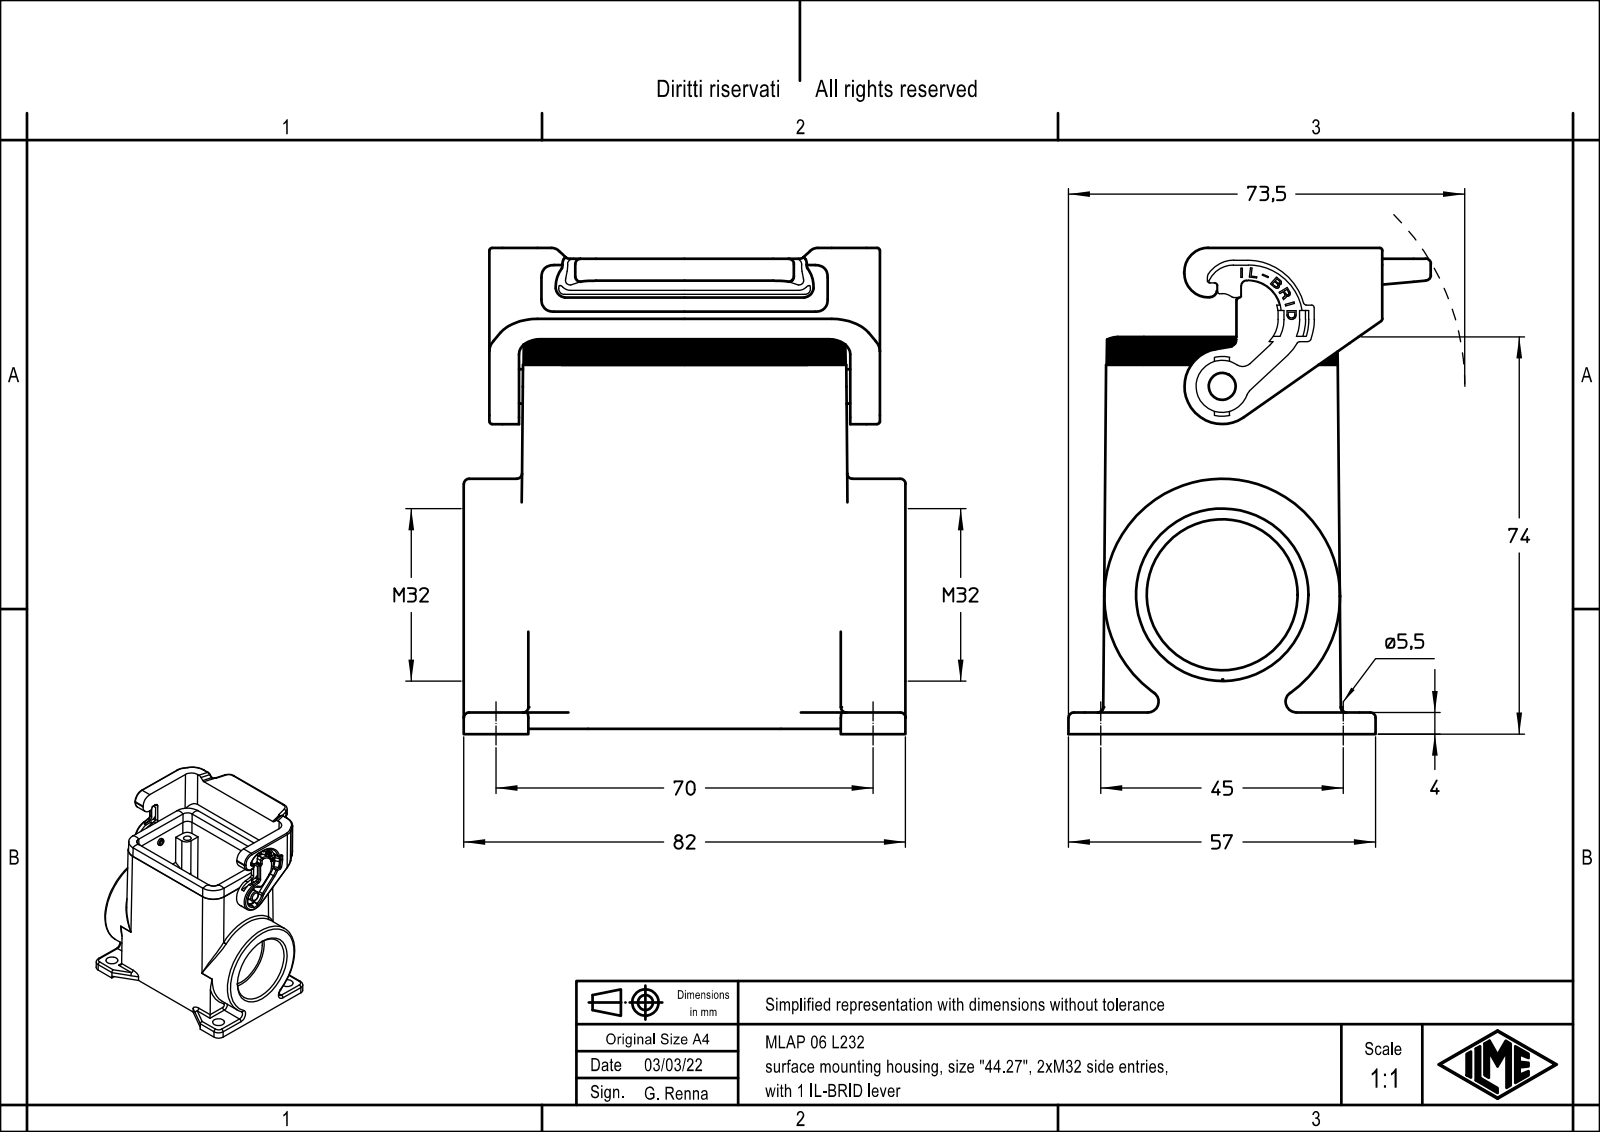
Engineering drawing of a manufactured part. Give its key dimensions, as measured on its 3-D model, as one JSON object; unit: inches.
{"part_name": "MLAP_06_L232", "step_written_by": "Creo Elements/Direct Modeling 20.1B 02-Apr-2019 (C) Parametric Technology GmbH (AUTOMOTIVE_DESIGN)", "units": "inches", "bodies": {"solids": 1, "faces": 708, "planar": 449, "cylindrical": 191, "other": 68}, "overall_size": [3.551, 3.228, 2.648], "volume_in3": 6.236, "surface_area_in2": 70.57, "round_holes": [[0.138, 4], [0.232, 4], [1.102, 1], [1.205, 1]], "round_bosses_or_shafts": [[1.693, 1], [0.252, 1], [0.189, 1]], "partial_cylinders_radius": [[0.039, 31], [0.118, 16], [0.059, 10], [0.079, 10], [0.276, 6], [0.012, 4], [0.122, 4], [0.157, 4]], "face_to_face_distances": [0.148, 1.545, 1.693, 1.398, 0.276, 0.157, 0.144, 0.03, 2.372, 0.856], "hole_center_spacings": [0.622, 1.507, 2.272, 2.654, 1.063, 1.732, 1.772, 2.032]}
